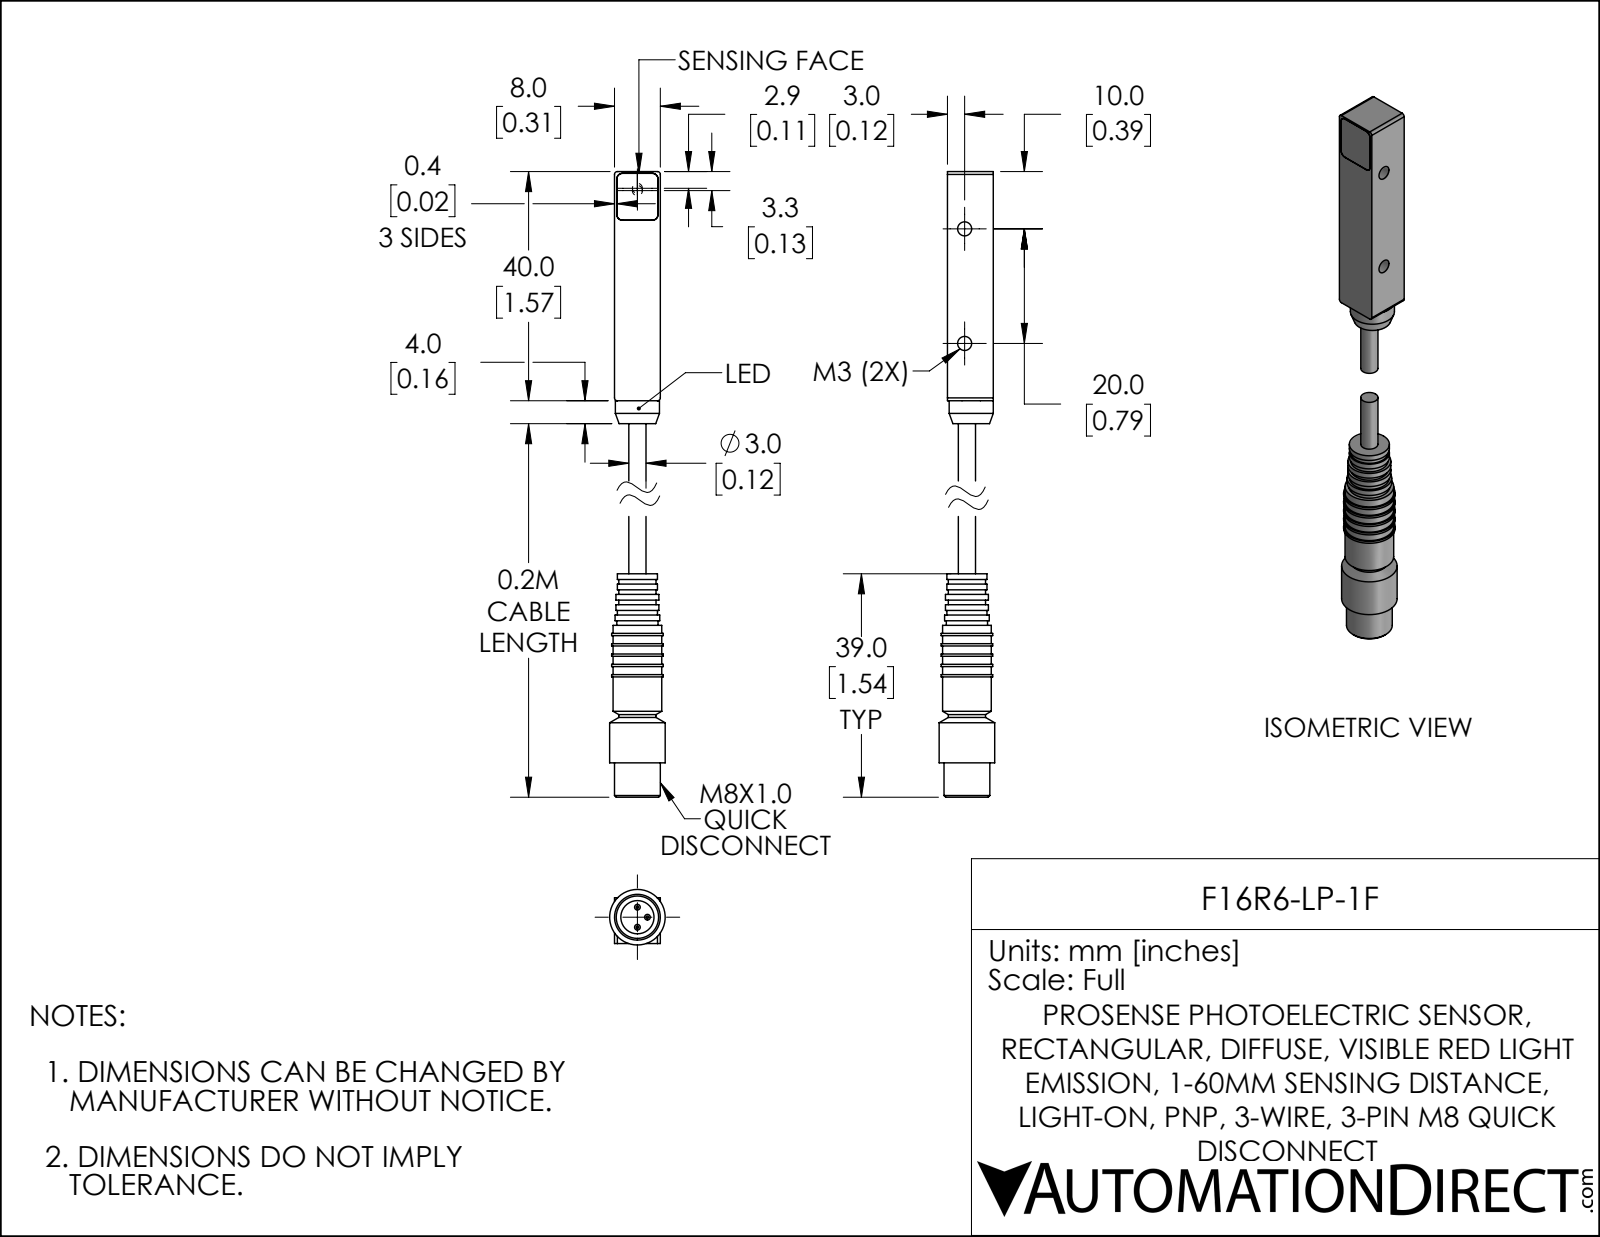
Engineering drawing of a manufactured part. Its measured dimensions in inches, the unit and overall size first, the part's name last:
Units: inches
Overall size (bounding box): 4.35 × 0.382 × 0.382
Round holes (diameter × count): ⌀0.097 ×2, ⌀0.228 ×1
Round bosses / shafts (diameter × count): ⌀0.039 ×3, ⌀0.382 ×1, ⌀0.354 ×1, ⌀0.335 ×1, ⌀0.315 ×1, ⌀0.307 ×1, ⌀0.303 ×1, ⌀0.295 ×1
Partial cylindrical surfaces — rounded edges, fillets, slot ends (radius × count): R0.02 ×4, R0.039 ×4, R0.039 ×4
Main face-to-face distances: 0.315, 0.071, 0.142, 0.039, 0.354, 1.732, 2.815, 2.421, 0.213, 1.083
Hole centre spacings: 0.787
Volume: 0.293 in³ · Surface area: 5.017 in²
Bodies: 2 solids, 102 faces (50 planar, 45 cylindrical, 7 other)
Part name (STEP PRODUCT): F16R6-LP-1F_1; F16R6-LP-1F_2; F16R6-LP-1F
STEP written by: SolidWorks 2019 (AUTOMOTIVE_DESIGN)
